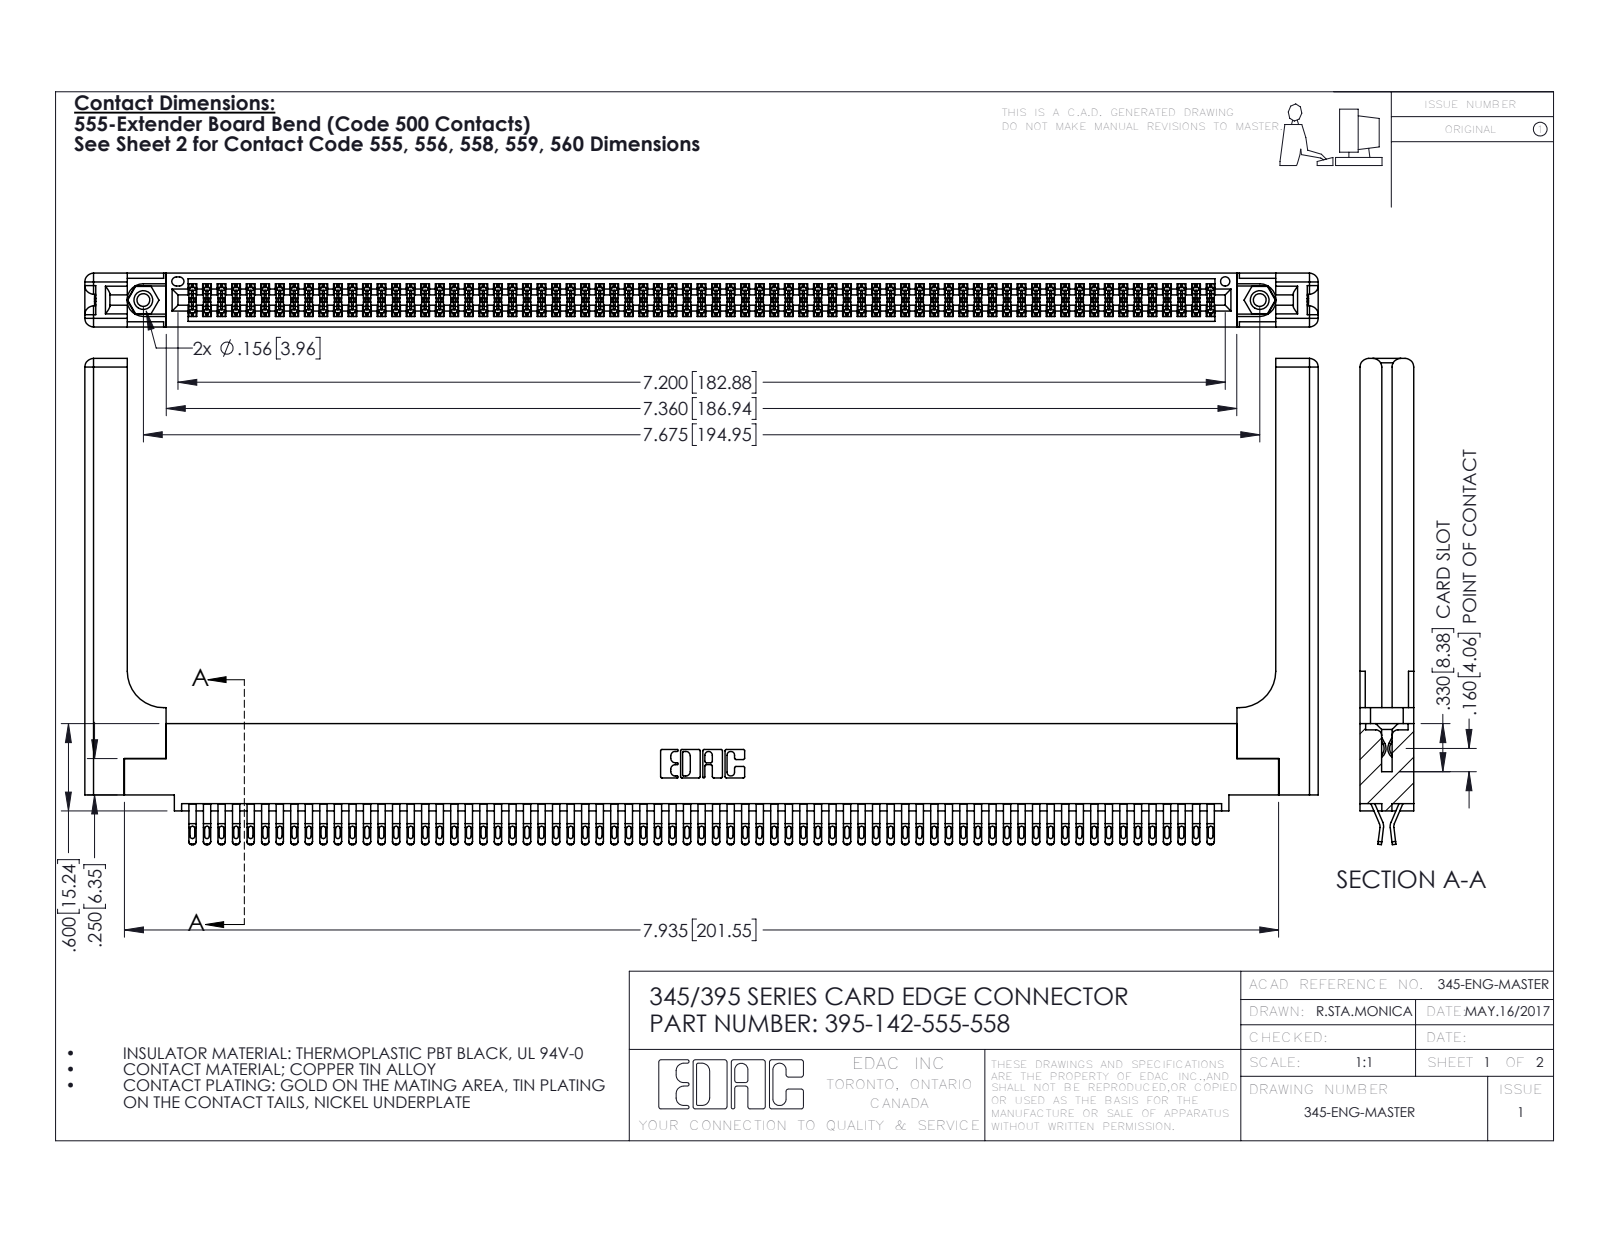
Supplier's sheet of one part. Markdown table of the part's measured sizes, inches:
| quantity | value |
| --- | --- |
| part name | 345-220-058_345-220-058; 395-142-555-558; 345-292-001_555 Tail; 345-250-001_345-250-001-102 (+1 more) |
| STEP written by | SolidWorks 2016 (CONFIG_CONTROL_DESIGN) |
| units | inches |
| bodies | 147 solids, 8338 faces (4634 planar, 3644 cylindrical, 60 other) |
| overall size | 8.479 × 3.342 × 0.37 |
| volume | 1.831 in³ |
| surface area | 60.4 in² |
| round holes (diameter × count) | 0.089 × 2, 0.125 × 2, 0.156 × 2, 0.064 × 1 |
| round bosses / shafts (diameter × count) | 0.155 × 2 |
| partial cylindrical surfaces (radius × count) | 0.016 × 355, 0.02 × 284, 0.006 × 213, 0.01 × 22, 0.06 × 16, 0.007 × 6, 0.031 × 6, 0.026 × 3 |
| main face-to-face distances | 0.072, 0.298, 0.37, 0.025, 0.098, 0.272, 0.2, 0.225, 0.175, 0.148 |
| hole center spacings | 0.27, 7.439, 7.675 |
